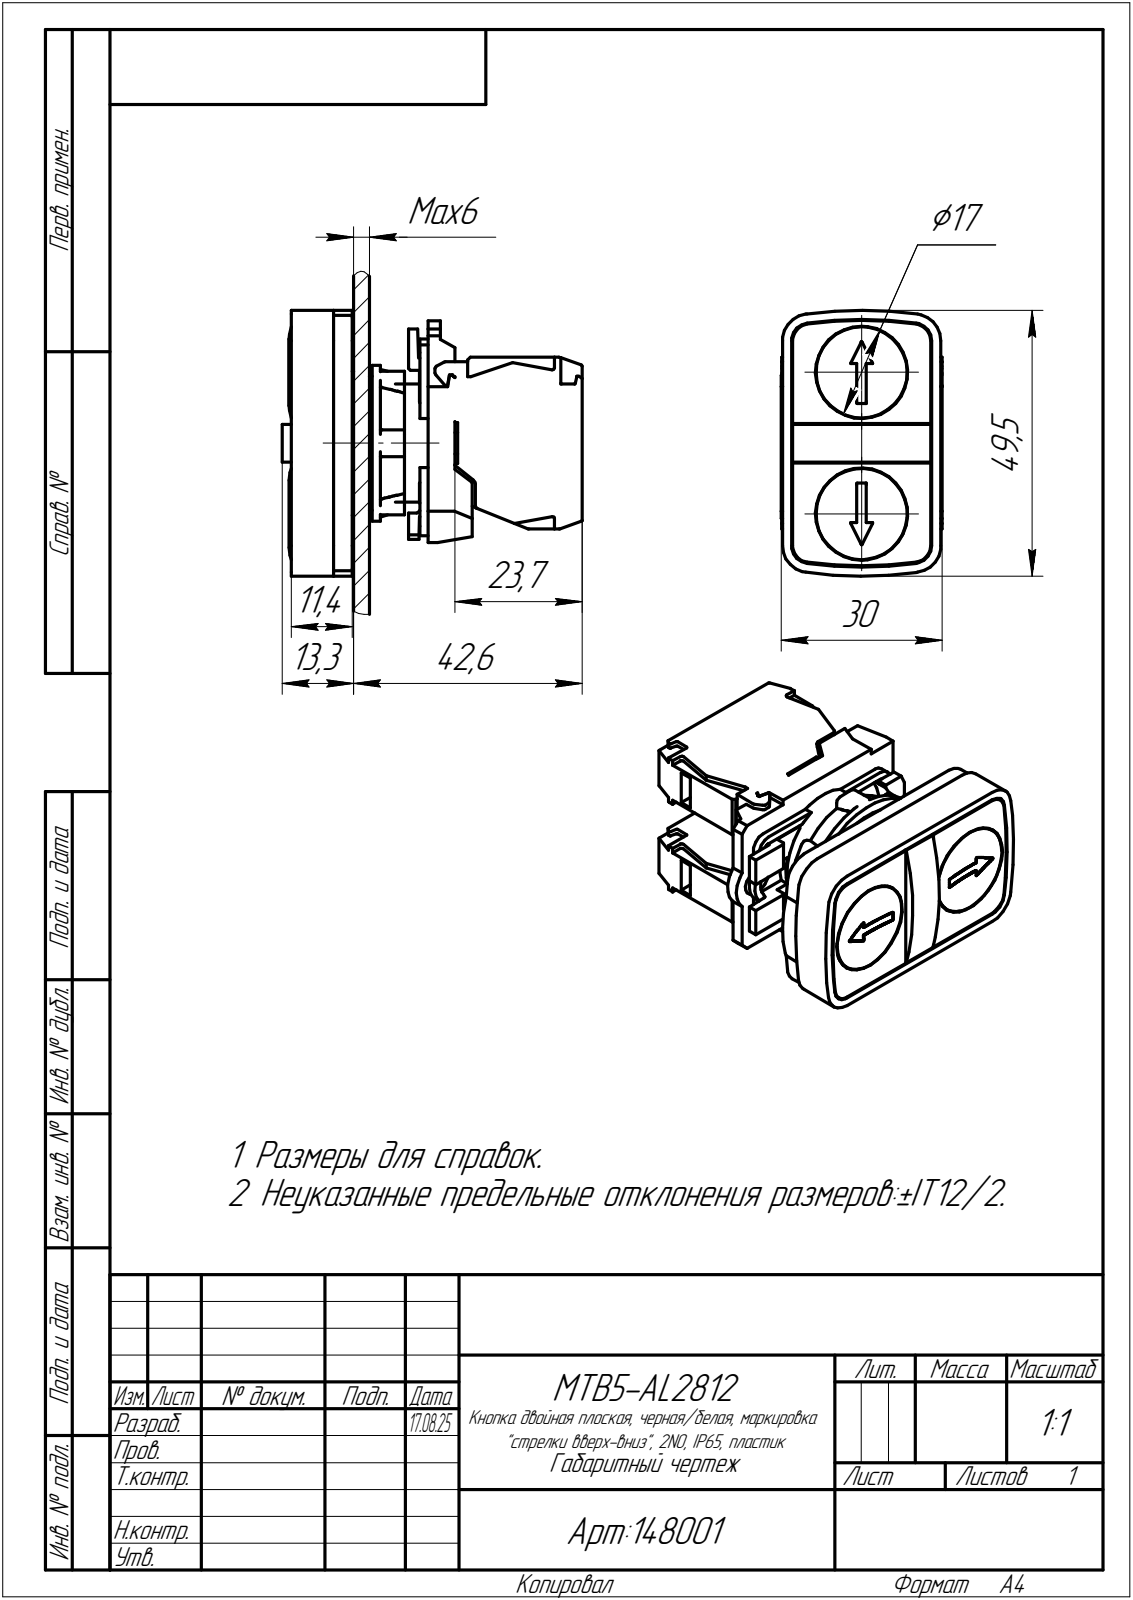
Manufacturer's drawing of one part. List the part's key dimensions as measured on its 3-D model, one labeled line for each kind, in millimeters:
Part name (STEP PRODUCT): MTB5-AL2812
STEP written by: C3D Toolkit (CONFIG_CONTROL_DESIGN)
Units: millimetres
Bodies: 1 solid, 532 faces (353 planar, 156 cylindrical, 23 other)
Overall size (bounding box): 55.9 × 49.5 × 30
Volume: 41 333 mm³ · Surface area: 16 536 mm²
Round holes (diameter × count): ⌀17.2 ×2, ⌀5.2 ×1, ⌀20.5 ×1
Round bosses / shafts (diameter × count): ⌀17 ×2, ⌀29 ×1, ⌀26.8 ×1, ⌀25 ×1, ⌀22 ×1
Partial cylindrical surfaces — rounded edges, fillets, slot ends (radius × count): R1 ×15, R0.2 ×13, R0.1 ×10, R0.5 ×7, R2.5 ×4, R3.1 ×4, R3.3 ×4, R4.35 ×4
Main face-to-face distances: 20, 9.9, 14.1, 25.5, 11.4, 10.1, 29.9, 9, 27.8, 1.7
Hole centre spacings: 13.2, 26.4
